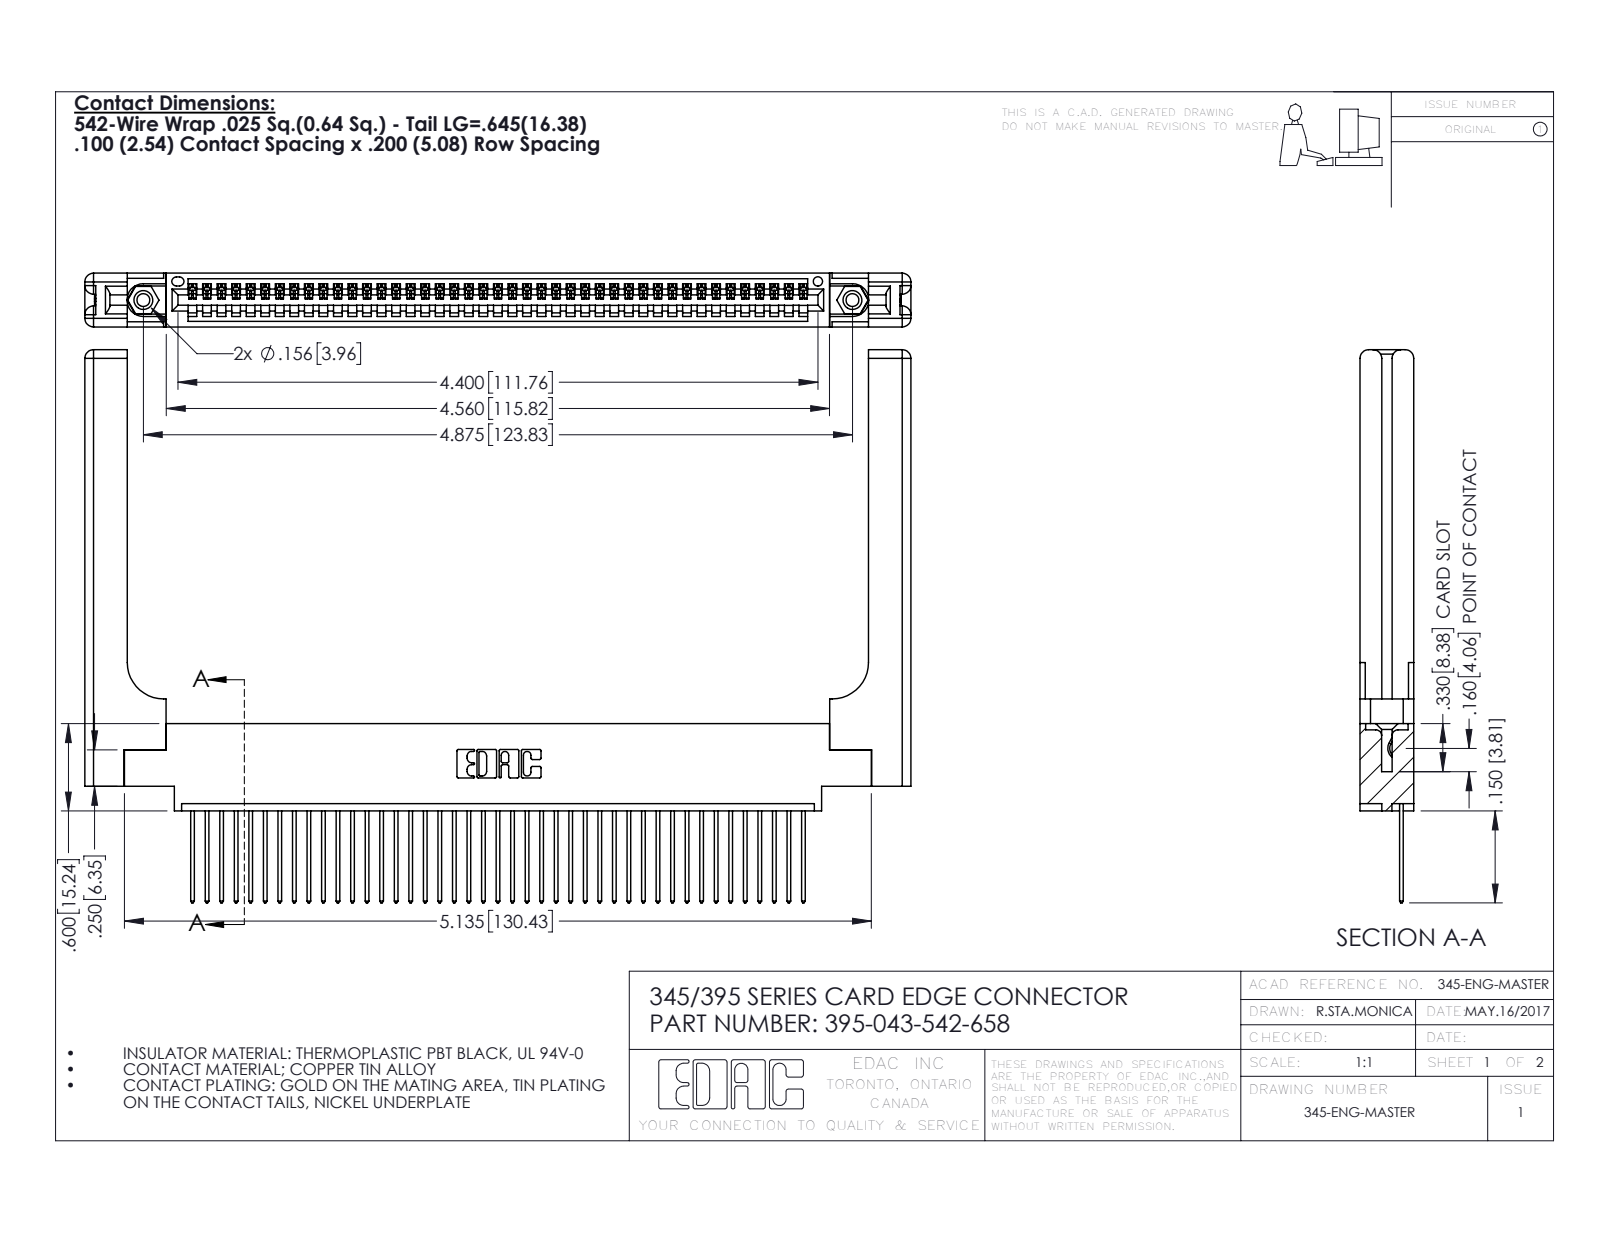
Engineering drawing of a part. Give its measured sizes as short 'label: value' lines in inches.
name: 395-043-542-658; 345-220-058_345-220-058; 345-250-001_345-250-001-102; 345-292-001_345-293-142 (+1 more)
written by: SolidWorks 2016 (CONFIG_CONTROL_DESIGN)
unit: in
bodies: 48 solids, 2880 faces (1952 planar, 868 cylindrical, 60 other)
size: 5.679 × 3.802 × 0.37
volume: 1.354 in³; area: 37.58 in²
holes: 2× ⌀0.089, 2× ⌀0.125, 2× ⌀0.156, 1× ⌀0.064
bosses: 2× ⌀0.155
rounds: 86× R0.006, 86× R0.01, 22× R0.01, 16× R0.06, 6× R0.007, 6× R0.031, 3× R0.026, 2× R0.03
face distances: 0.072, 0.37, 0.298, 0.098, 0.272, 0.025, 0.2, 0.225, 0.148, 0.15
hole spacings: 0.27, 4.639, 4.875
